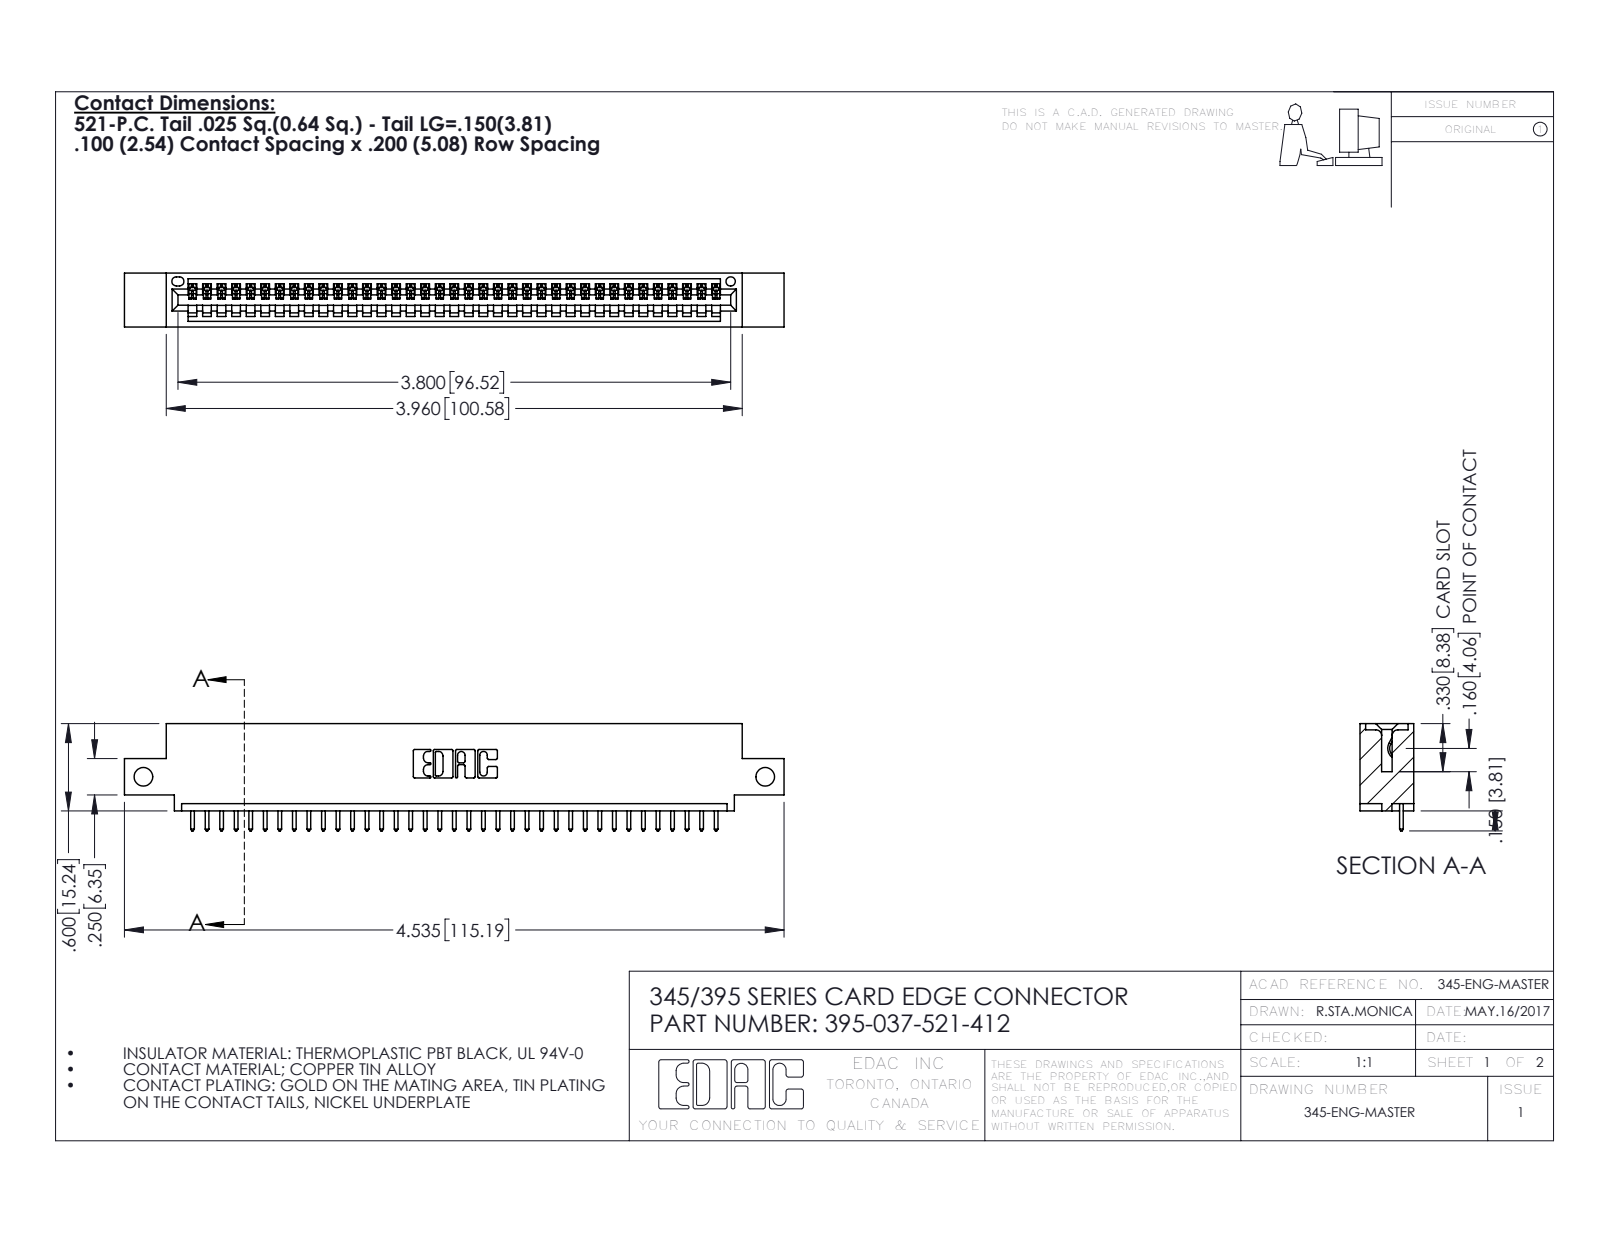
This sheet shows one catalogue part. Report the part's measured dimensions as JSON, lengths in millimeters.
{"part_name": "395-037-521-412; 345-292-001_345-293-121; 345 Part_0.110 Offset - Side Mount", "step_written_by": "SolidWorks 2016 (CONFIG_CONTROL_DESIGN)", "units": "millimeters", "bodies": {"solids": 38, "faces": 2276, "planar": 1564, "cylindrical": 712, "other": 0}, "overall_size": [115.2, 18.7, 9.4], "volume_mm3": 10600, "surface_area_mm2": 13590, "round_holes": [[3.3, 2], [1.6, 1]], "partial_cylinders_radius": [[0.2, 74], [0.3, 74], [0.3, 22], [0.2, 6], [0.8, 6], [0.7, 3], [0.8, 2], [1, 2]], "face_to_face_distances": [7.6, 1.8, 9.4, 5.1, 2.5, 6.9, 0.6, 5.7, 3.8, 1.8], "hole_center_spacings": [108.6]}
